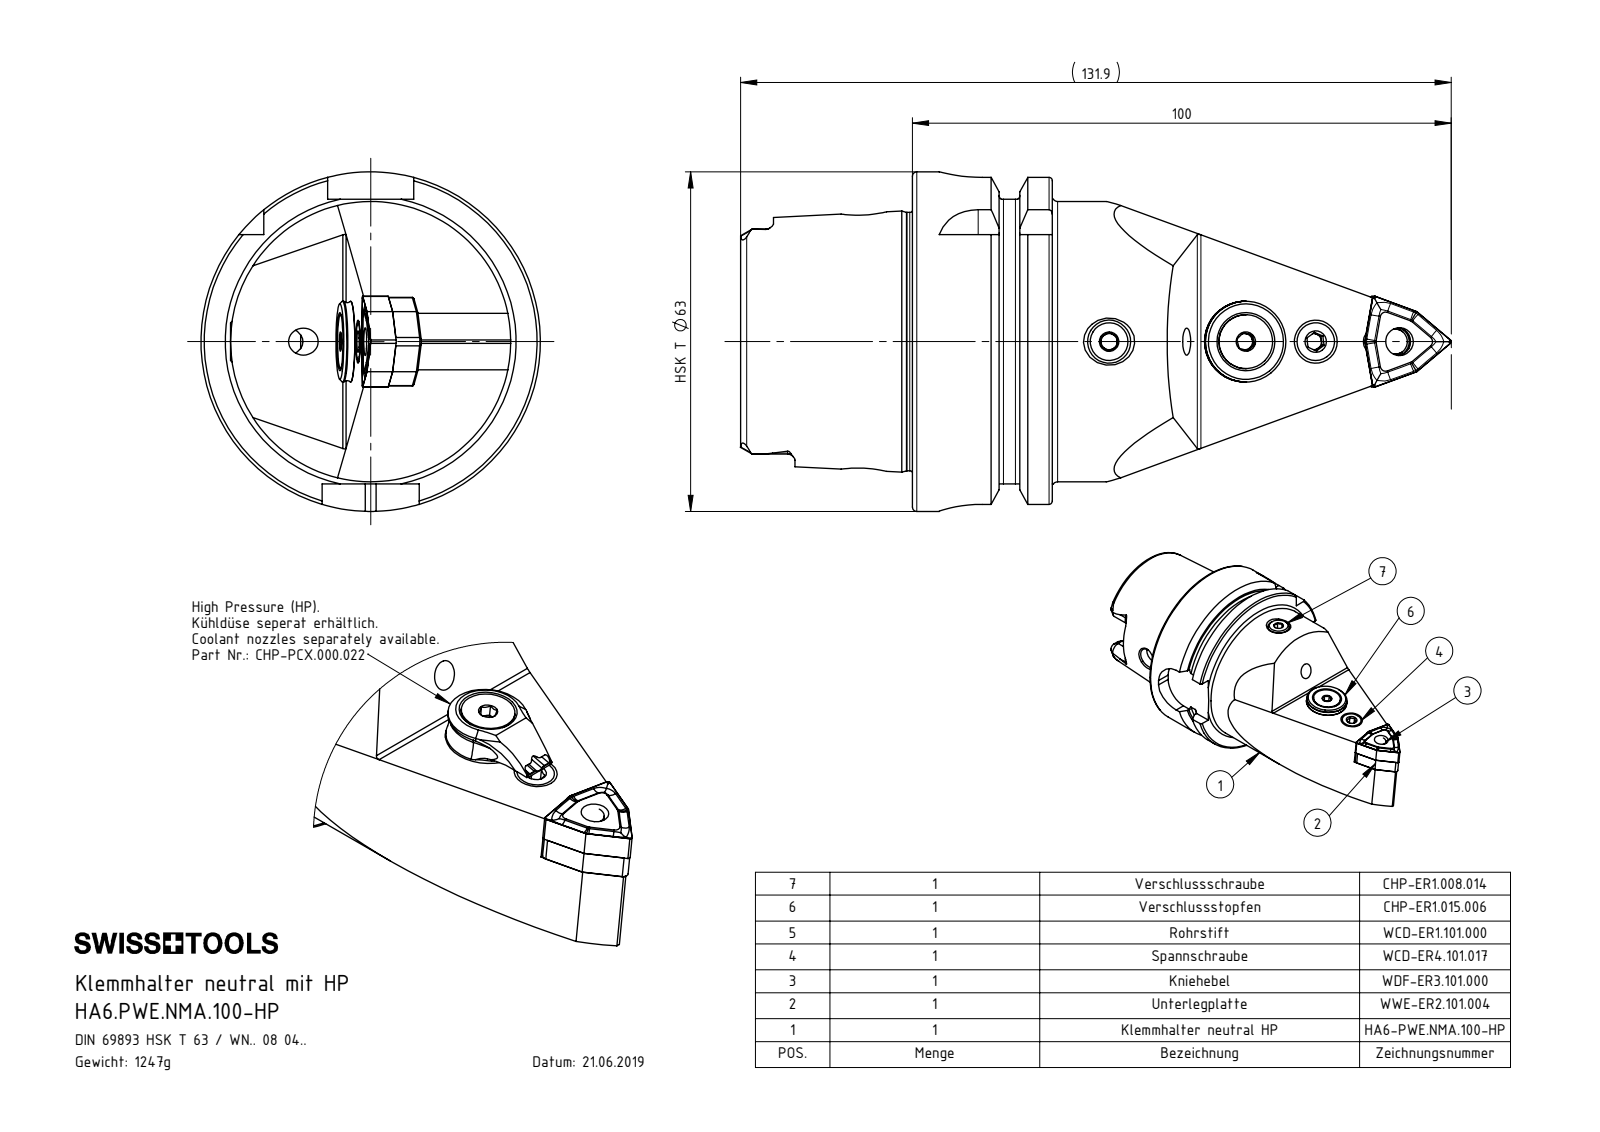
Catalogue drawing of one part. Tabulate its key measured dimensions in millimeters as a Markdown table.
| quantity | value |
| --- | --- |
| part name | ISO 8752 2x8; WCD-ER4.101.017_A; CHP-ER1.008.014_A; DIN 3771 - 13x1 (+8 more) |
| STEP written by | SolidWorks 2017 (AUTOMOTIVE_DESIGN) |
| units | millimeters |
| bodies | 11 solids, 506 faces (165 planar, 135 cylindrical, 206 other) |
| overall size | 131.9 × 63 × 63 |
| volume | 158 575 mm³ |
| surface area | 36 526 mm² |
| round holes (diameter × count) | 5 × 3, 4.2 × 2, 7 × 2, 8.4 × 2, 1.2 × 1, 2 × 1, 2.5 × 1, 3 × 1, 5.16 × 1, 5.2 × 1, 6.7 × 1, 7.5 × 1 |
| round bosses / shafts (diameter × count) | 8 × 2, 63 × 1, 54.95 × 1, 52 × 1, 47.94 × 1, 15 × 1, 13.4 × 1, 10 × 1 |
| partial cylindrical surfaces (radius × count) | 1.4 × 6, 2.88 × 4, 8 × 4, 0.4 × 3, 1 × 3, 2.5 × 3, 0.8 × 1, 2.3 × 1 |
| main face-to-face distances | 25.95, 16, 9.95, 31.9, 41.85, 57.85, 52.8, 21.8, 11.85, 4.5 |
| hole center spacings | 4.5, 4.51, 4.52, 4.53, 10.13, 10.14, 13.24, 13.26 |
